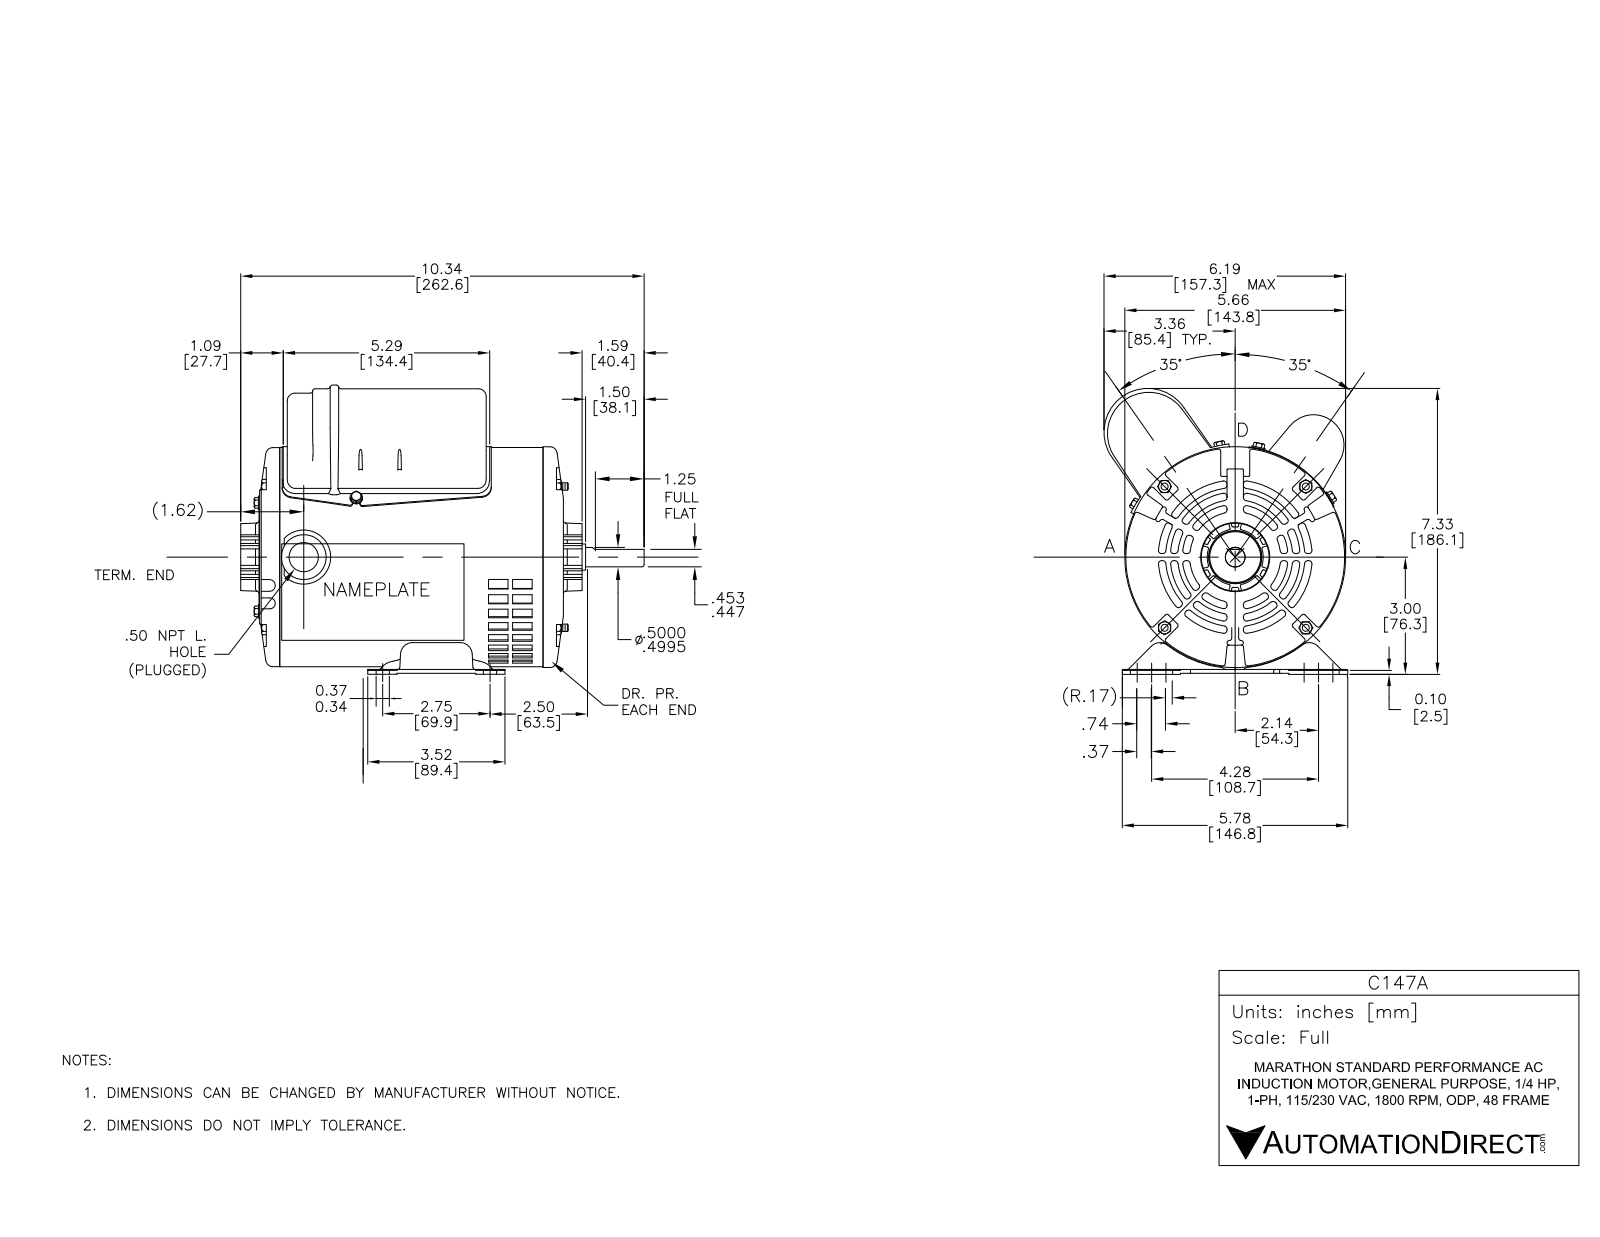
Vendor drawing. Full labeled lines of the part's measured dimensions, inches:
Part name (STEP PRODUCT): C147A SS404113-675_RevB
STEP written by: SolidWorks 2017 (AUTOMOTIVE_DESIGN)
Units: inches
Bodies: 29 solids, 4074 faces (1318 planar, 770 cylindrical, 1986 other)
Overall size (bounding box): 10.34 × 7.066 × 6.049
Volume: 27.51 in³ · Surface area: 680 in²
Round holes (diameter × count): ⌀0.153 ×11, ⌀0.38 ×6, ⌀0.25 ×5, ⌀0.193 ×4, ⌀0.22 ×4, ⌀0.218 ×2, ⌀0.457 ×1, ⌀0.505 ×1, ⌀0.64 ×1, ⌀0.669 ×1, ⌀0.687 ×1, ⌀0.73 ×1
Round bosses / shafts (diameter × count): ⌀0.164 ×6, ⌀0.399 ×4, ⌀0.348 ×4, ⌀0.19 ×4, ⌀0.166 ×4, ⌀0.335 ×2, ⌀5.62 ×1, ⌀5.615 ×1
Partial cylindrical surfaces — rounded edges, fillets, slot ends (radius × count): R0.06 ×52, R0.03 ×44, R0.015 ×32, R0.02 ×27, R0.25 ×25, R0.01 ×24, R0.05 ×20, R0.12 ×19
Main face-to-face distances: 0.026, 0.04, 7.41, 0.105, 5.116, 0.06, 0.104, 7.45, 0.08, 0.025
Hole centre spacings: 2.562, 3.624, 1.12, 1.19, 2.4, 2.578, 4.243, 4.82
